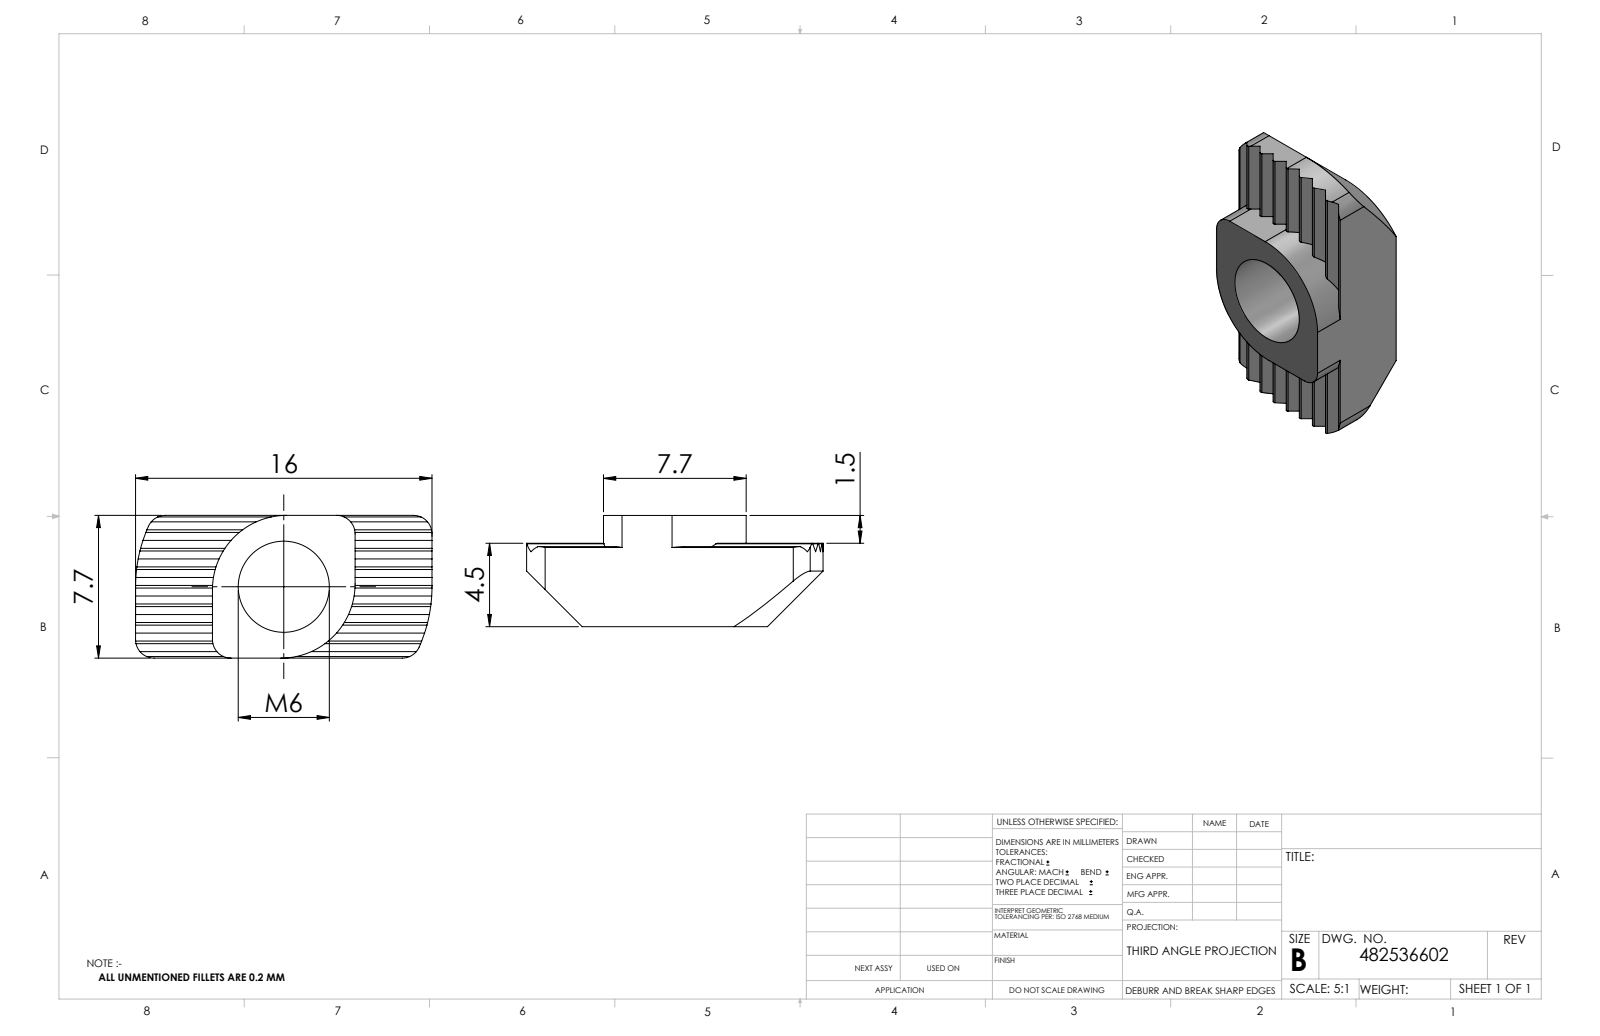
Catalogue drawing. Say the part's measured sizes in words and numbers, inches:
The part is named "482536602_c_1". Its 3-D file was written by "SolidWorks 2014 (CONFIG_CONTROL_DESIGN)". It is 1 solid with 74 faces: 42 planar, 30 cylindrical and 2 other. Overall it measures 0.63 by 0.303 by 0.236 inches. Its volume is 0.026 cubic inches and its surface area 0.795 square inches. Round holes: 1 of diameter 0.194. Partial cylindrical surfaces (rounded edges, fillets, slot ends): 7 of radius 0.004, 6 of radius 0.039, 2 of radius 0.157, 1 of radius 0.315. The main face-to-face distances are 0.303, 0.028, 0.083, 0.056, 0.236, 0.111, 0.139, 0.028, 0.167, 0.056.
